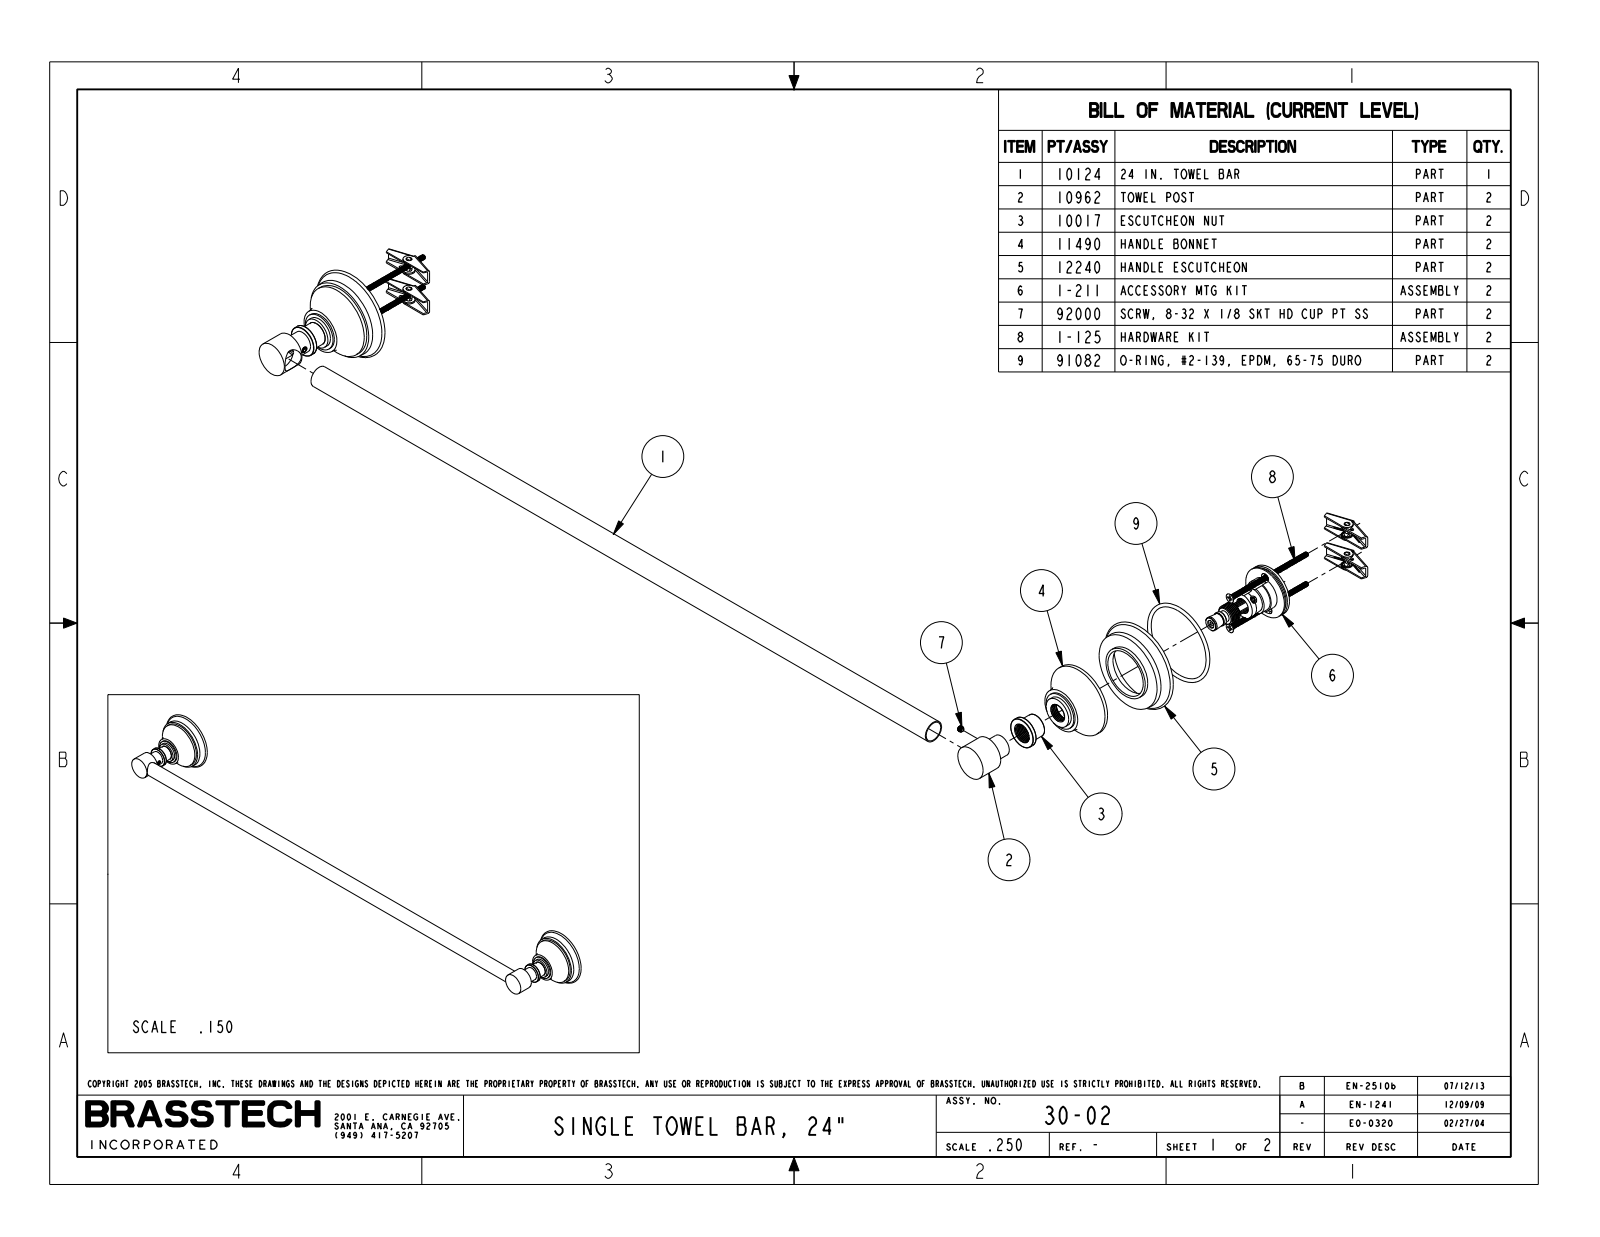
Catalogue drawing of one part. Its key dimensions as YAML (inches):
part_name: "30-02_WEB"
step_written_by: "PRO/ENGINEER BY PARAMETRIC TECHNOLOGY CORPORATION, 2009300 (CONFIG_CONTROL_DESIGN)"
units: inches
bodies: {solids: 0, faces: 82, planar: 18, cylindrical: 30, other: 34}
overall_size: [26.858, 3.203, 2.625]
round_bosses_or_shafts:
  - {diameter: 0.625, count: 3}
  - {diameter: 2.1, count: 2}
  - {diameter: 1.075, count: 2}
  - {diameter: 0.98, count: 2}
  - {diameter: 0.875, count: 2}
  - {diameter: 0.673, count: 2}
face_to_face_distances: [0.475, 1.225, 0.75, 1.275, 0.8, 0.05, 2.436, 1.961, 1.211, 1.161]
